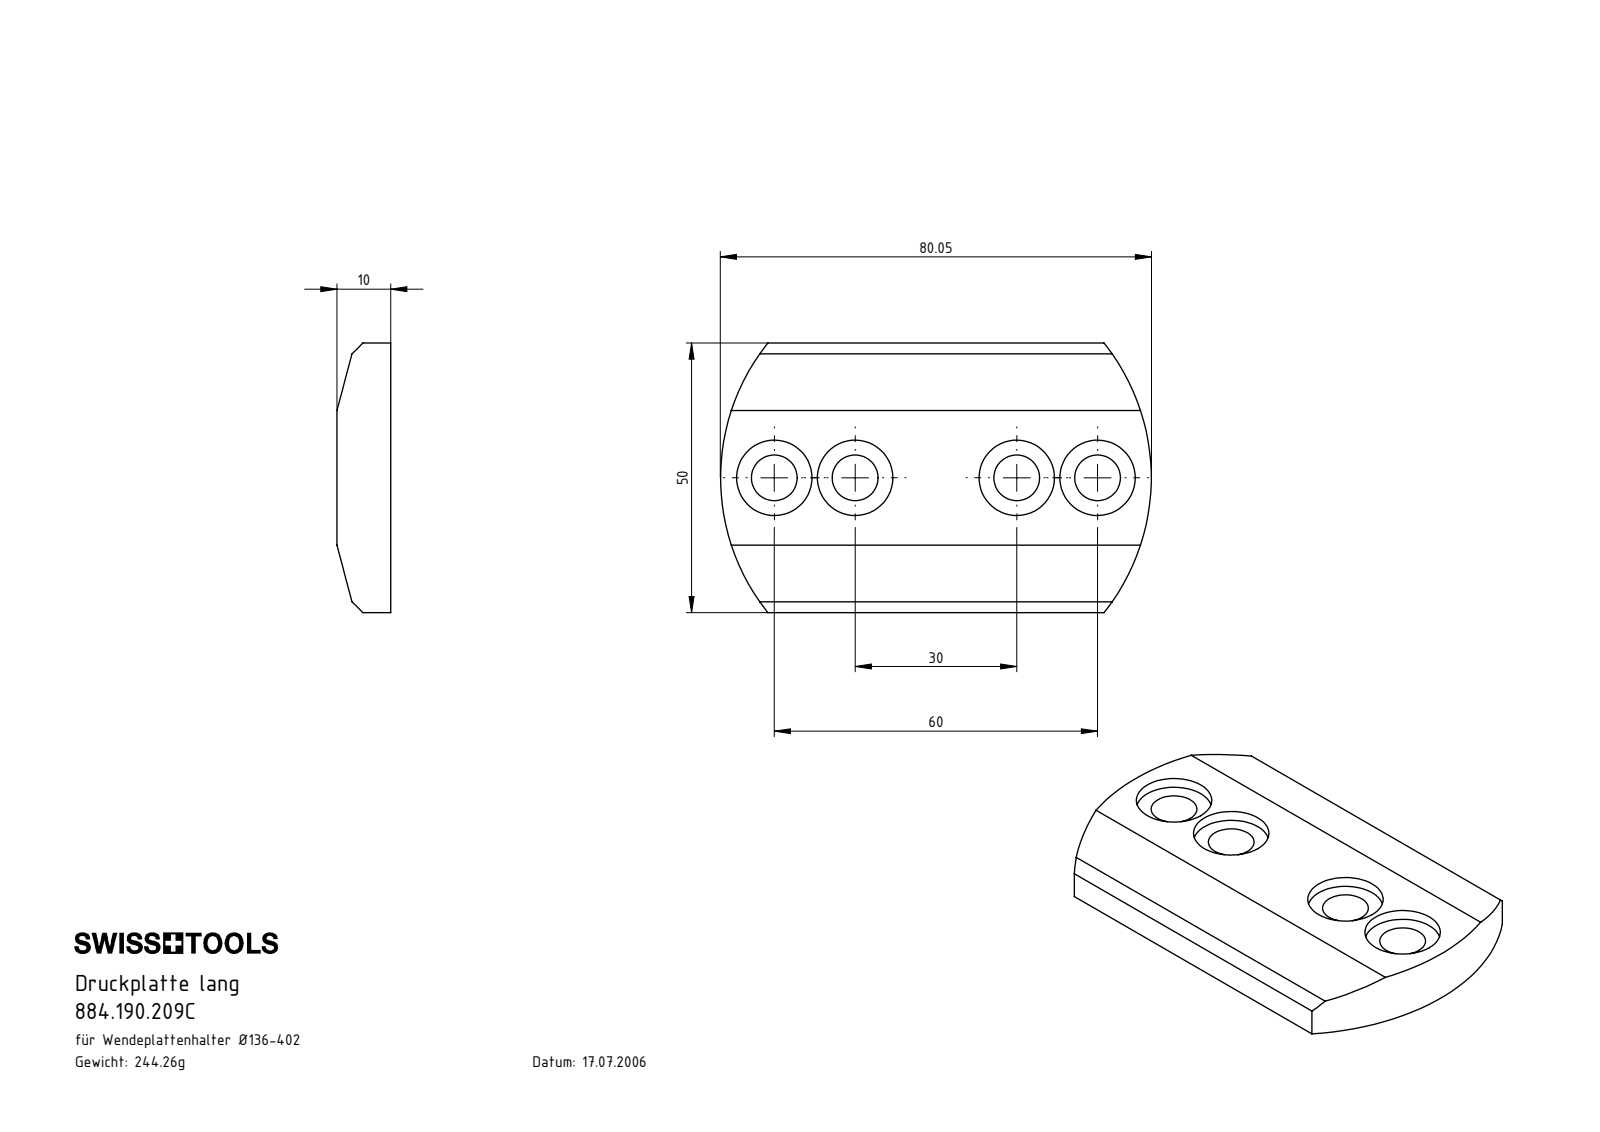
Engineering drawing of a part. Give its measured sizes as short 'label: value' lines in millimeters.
name: 884.190.209C
written by: SolidWorks 2022 (AUTOMOTIVE_DESIGN)
unit: mm
bodies: 1 solid, 30 faces (12 planar, 18 cylindrical, 0 other)
size: 79.95 × 50 × 10
volume: 31 116 mm³; area: 9 971 mm²
holes: 4× ⌀8.5, 4× ⌀14
rounds: 2× R40
face distances: 10, 8, 2, 50
hole spacings: 15, 45, 30, 60
